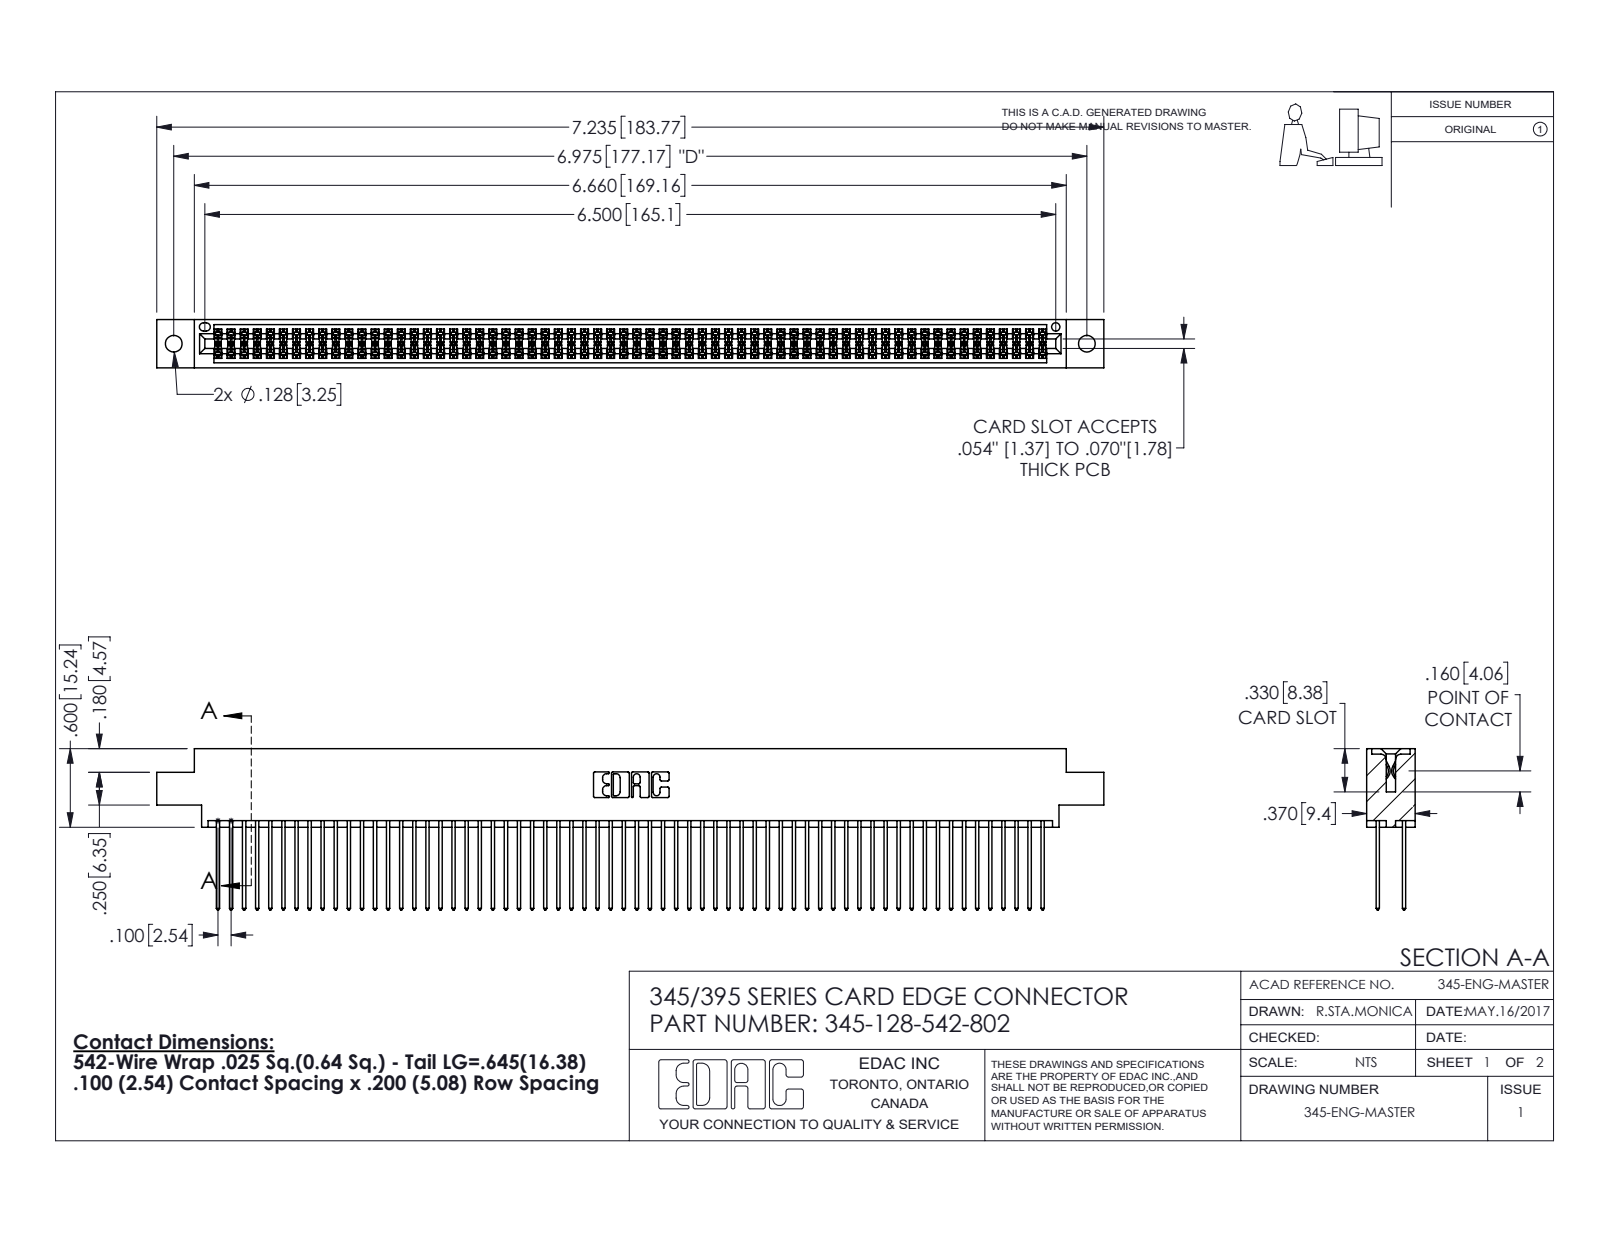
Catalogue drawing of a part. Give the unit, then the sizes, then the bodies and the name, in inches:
Units: inches
Overall size (bounding box): 7.235 × 1.232 × 0.37
Round holes (diameter × count): ⌀0.128 ×2, ⌀0.064 ×1
Partial cylindrical surfaces — rounded edges, fillets, slot ends (radius × count): R0.006 ×192, R0.01 ×128, R0.01 ×22, R0.007 ×6, R0.031 ×6, R0.026 ×3, R0.014 ×2, R0.019 ×2
Main face-to-face distances: 0.298, 0.072, 0.2, 0.098, 0.272, 0.025, 0.37, 0.225, 0.175, 0.149
Hole centre spacings: 0.27, 6.739, 6.975
Volume: 1.129 in³ · Surface area: 47.17 in²
Bodies: 129 solids, 6530 faces (4308 planar, 2222 cylindrical, 0 other)
Part name (STEP PRODUCT): 345 Part_0.170 Offset - 0.128 Dia; 345-128-542-802; 345-292-001_345-293-142
STEP written by: SolidWorks 2016 (CONFIG_CONTROL_DESIGN)
